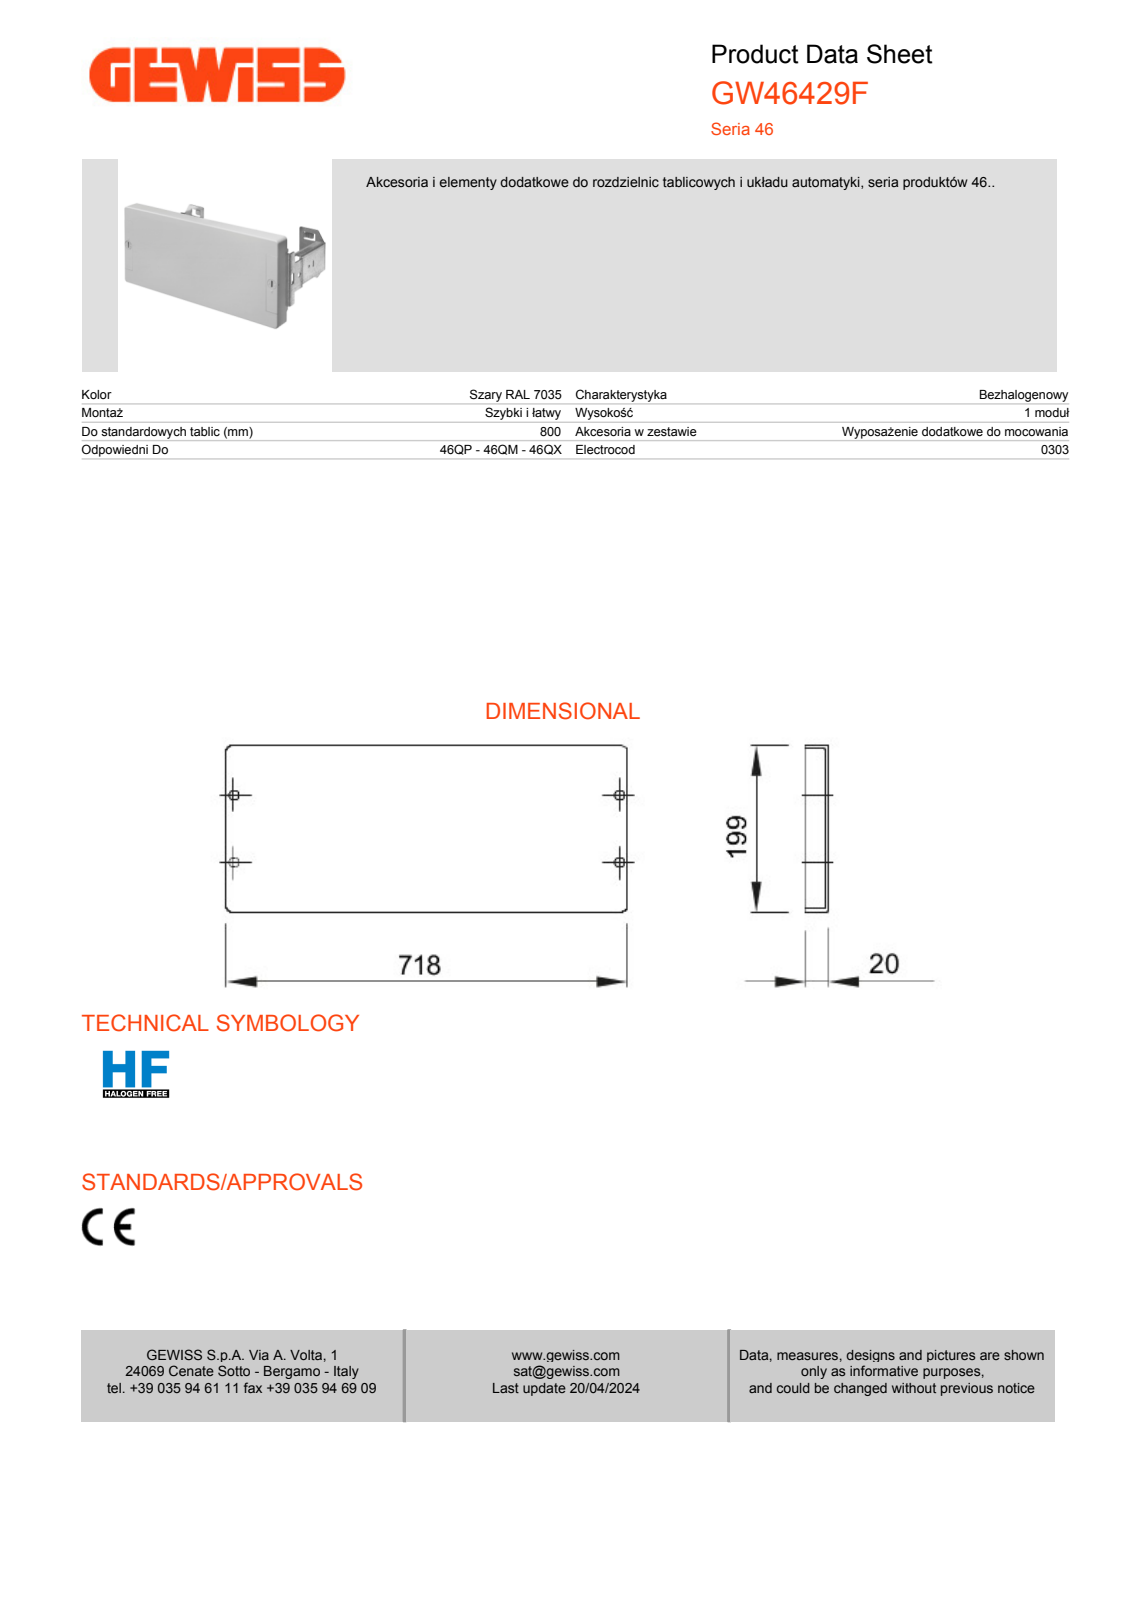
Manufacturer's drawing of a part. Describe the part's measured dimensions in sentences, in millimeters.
The part is named "55711006E2XX_MOSTRINA_CIECA_36M; 55718951FXXX_STAFFA_X_SUPP_GUID; STAFFE_29_ASM; GW46429F_ASM". Its 3-D file was written by "CREO PARAMETRIC BY PTC INC, 2020354 (CONFIG_CONTROL_DESIGN)". It is 3 solids with 540 faces: 338 planar, 146 cylindrical and 56 other. Overall it measures 723 by 199.18 by 119.87 millimeters. Its volume is 604 532 cubic millimeters and its surface area 428 672 square millimeters. Round holes: 4 of diameter 4.5, 4 of diameter 6.5, 2 of diameter 5.5, 1 of diameter 8. Round bosses or shafts: 2 of diameter 14.4, 2 of diameter 13.4, 2 of diameter 9.6. Partial cylindrical surfaces (rounded edges, fillets, slot ends): 28 of radius 1.5, 20 of radius 1, 4 of radius 1.15, 4 of radius 2, 2 of radius 0.5, 2 of radius 1.25, 2 of radius 2.5, 2 of radius 4. The main face-to-face distances are 3, 1.5, 30, 4, 713.5, 112, 115, 85, 27, 113.5. The hole center spacings are 30.23, 35.11, 686.91, 701.39, 14.5, 60, 682.5, 704.5.
